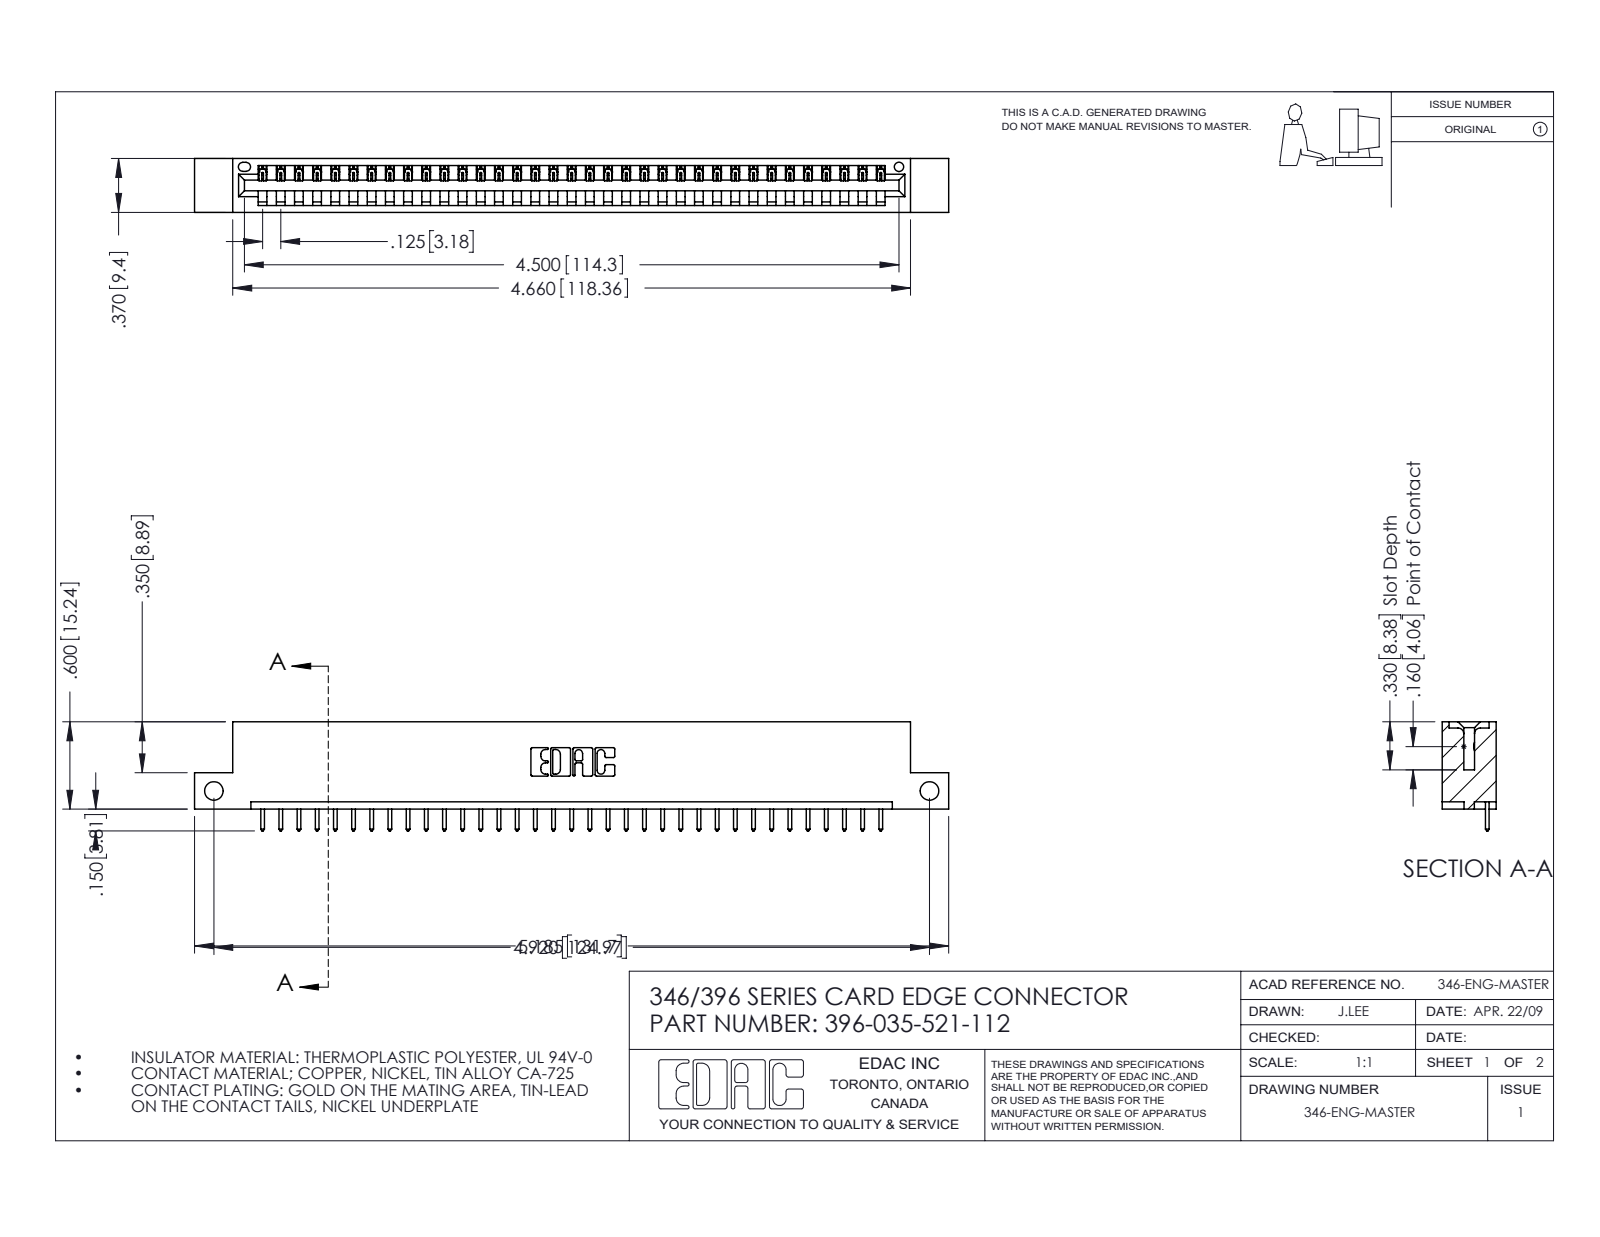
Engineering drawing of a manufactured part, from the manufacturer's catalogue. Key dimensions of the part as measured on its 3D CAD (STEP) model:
Part name (STEP PRODUCT): 396-035-521-112; 345-292-001_345-293-121; 346 Part_Flush Mounting Lugs - Side Mount
STEP written by: SolidWorks 2016 (CONFIG_CONTROL_DESIGN)
Units: inches
Bodies: 36 solids, 2152 faces (1476 planar, 676 cylindrical, 0 other)
Overall size (bounding box): 5.185 × 0.75 × 0.37
Volume: 0.755 in³ · Surface area: 23.01 in²
Round holes (diameter × count): ⌀0.128 ×2, ⌀0.064 ×1
Partial cylindrical surfaces — rounded edges, fillets, slot ends (radius × count): R0.006 ×70, R0.01 ×70, R0.01 ×22, R0.007 ×6, R0.031 ×6, R0.026 ×3, R0.031 ×2, R0.04 ×2
Main face-to-face distances: 0.048, 0.322, 0.37, 0.25, 0.072, 0.298, 0.025, 0.148, 0.222, 0.1
Hole centre spacings: 4.92
